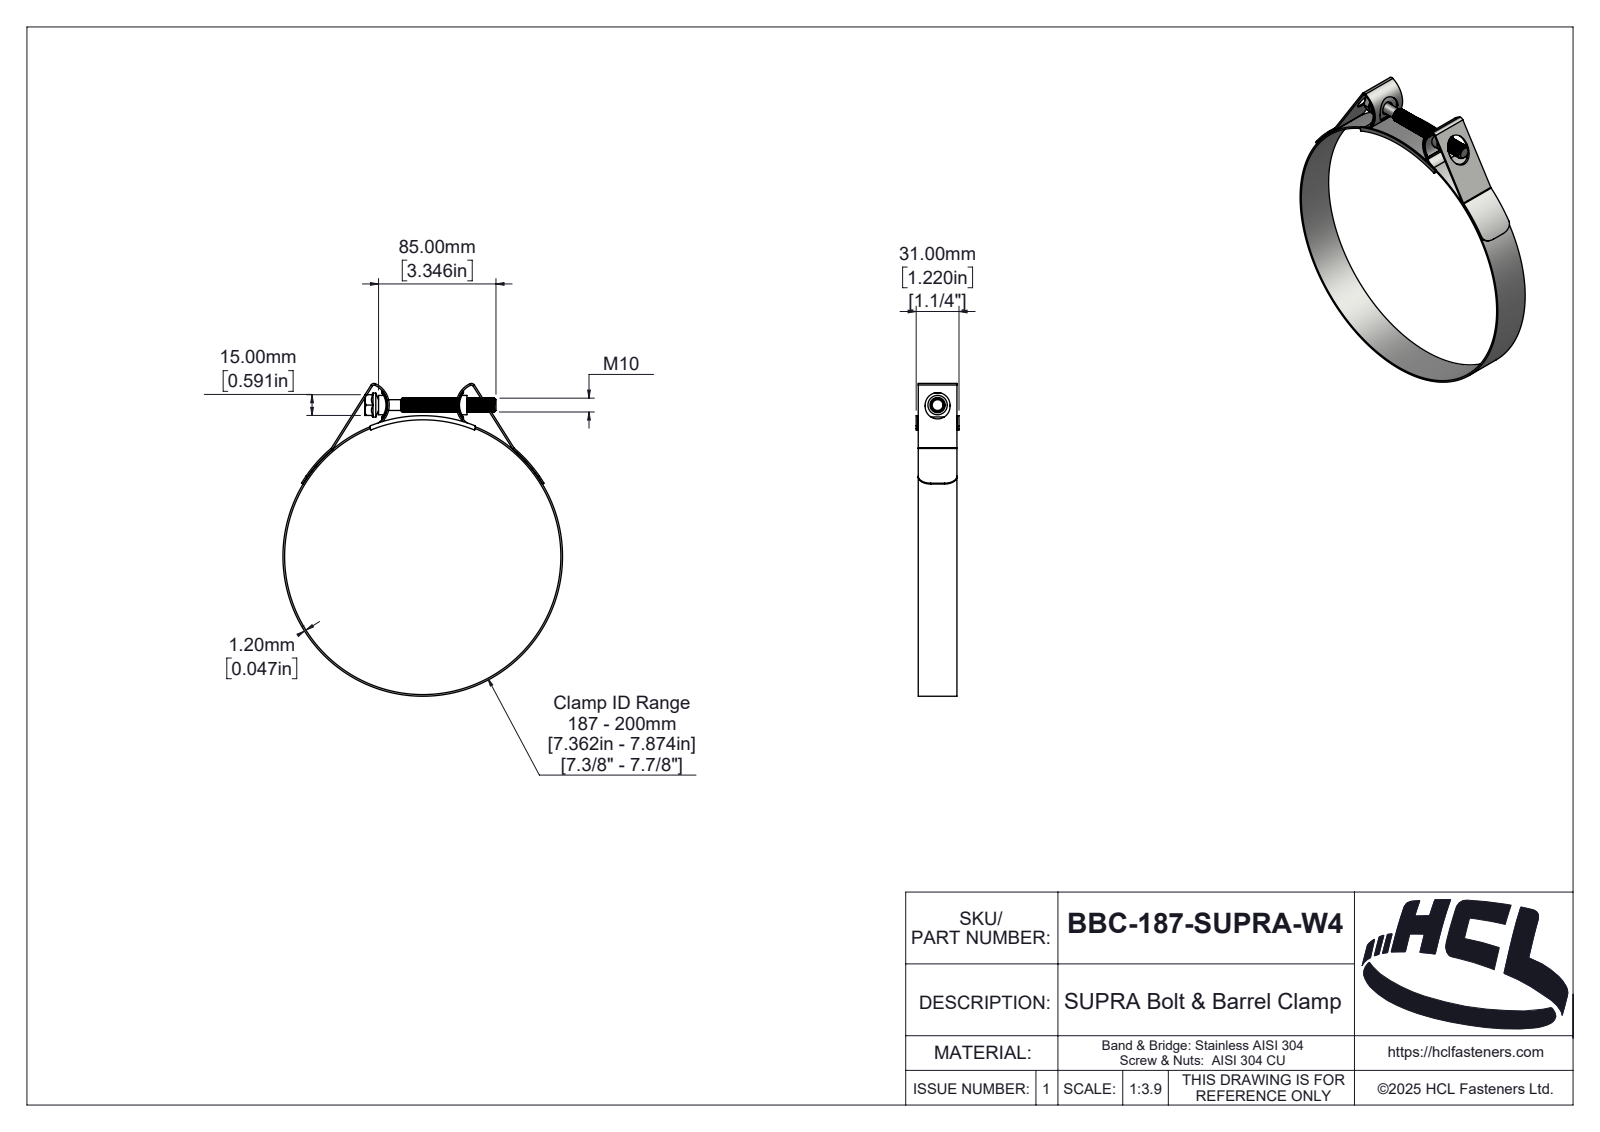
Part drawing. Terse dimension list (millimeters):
name: BBC-187-SUPRA-W4
written by: SolidWorks 2025 (AUTOMOTIVE_DESIGN)
unit: mm
bodies: 5 solids, 384 faces (50 planar, 247 cylindrical, 87 other)
size: 226.34 × 202.4 × 31
volume: 38 424 mm³; area: 58 776 mm²
holes: 1× ⌀200
bosses: 1× ⌀202.4, 1× ⌀17.32, 1× ⌀14, 1× ⌀10, 1× ⌀7.8
rounds: 4× R1, 2× R1.3, 2× R2, 2× R2.5, 2× R3.2, 2× R9, 2× R14.68, 2× R15.68
face distances: 1.2, 28, 1.5, 29.5, 29.8, 28.3, 31, 28.6, 15, 2.5
